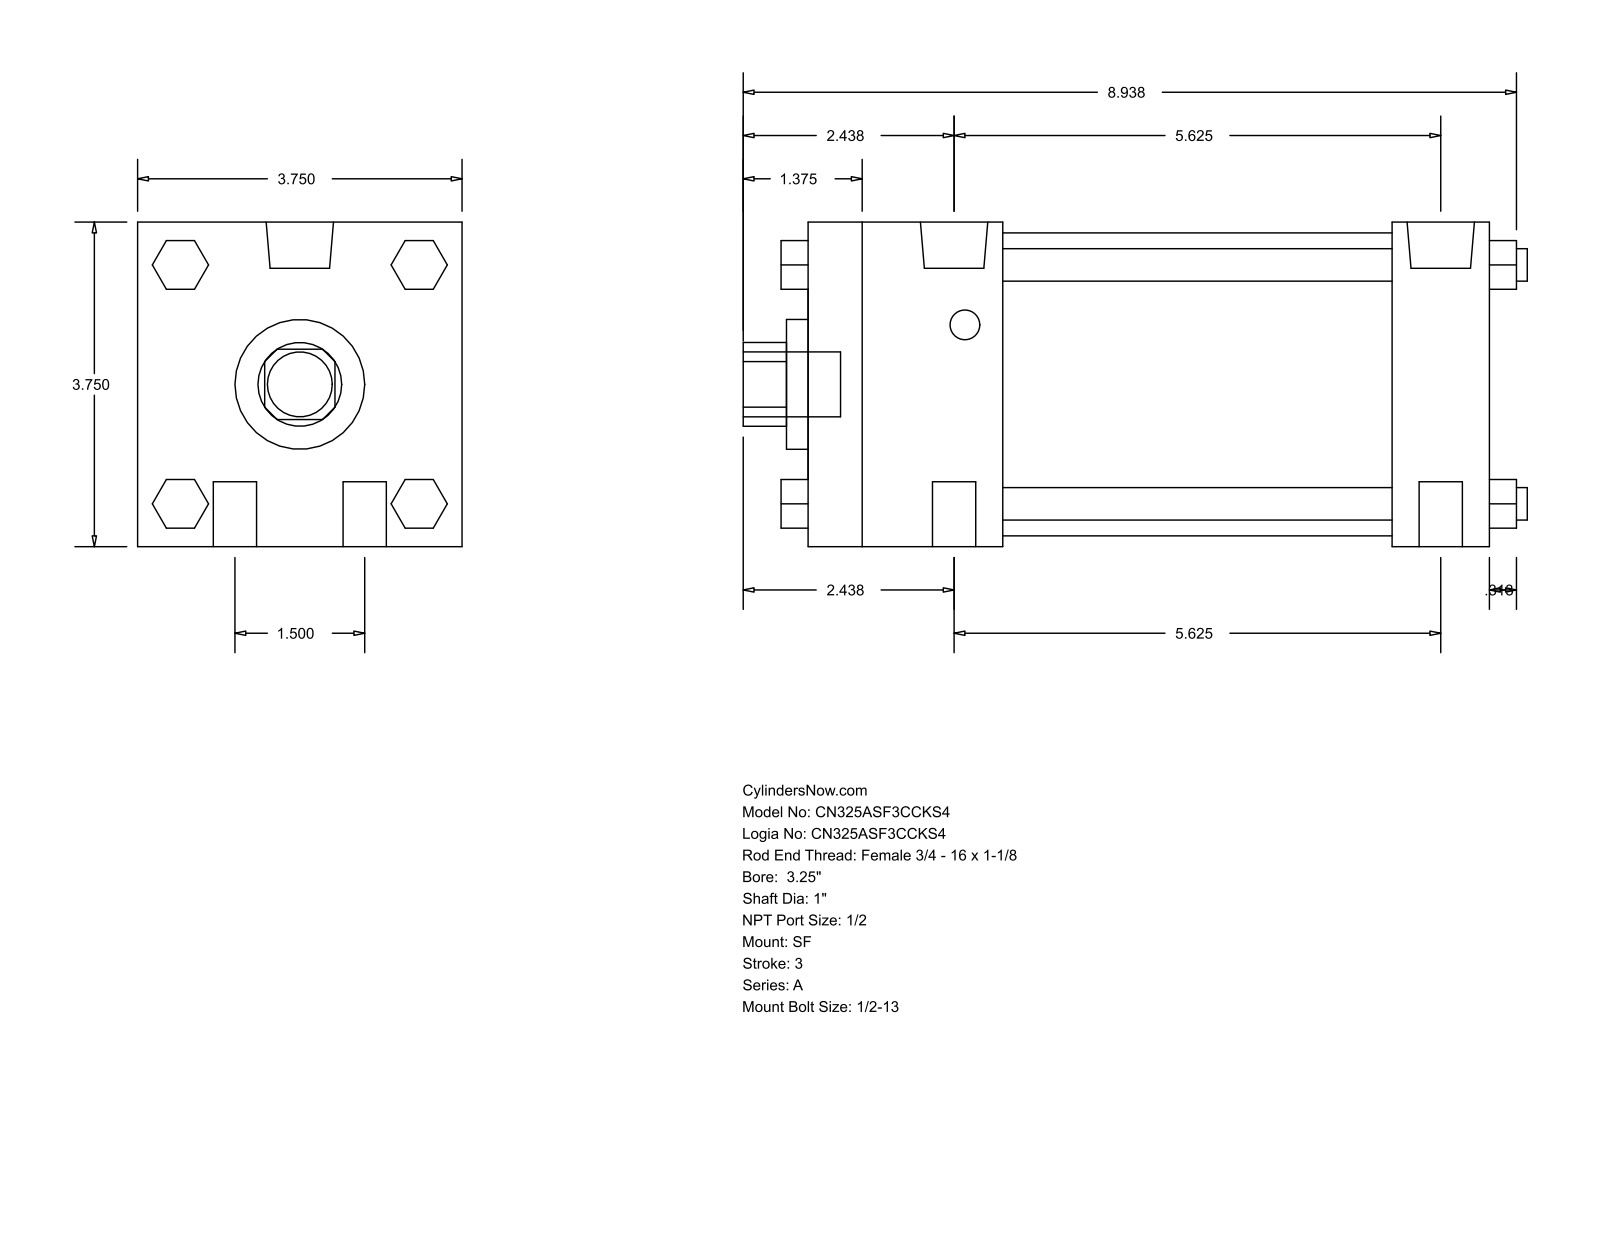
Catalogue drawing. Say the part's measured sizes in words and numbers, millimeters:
The part is named "A_SF__0325_1". Its 3-D file was written by "GSSL Pune (CONFIG_CONTROL_DESIGN)". It is 0 solids with 124 faces: 94 planar, 30 cylindrical and 0 other. Overall it measures 230.19 by 95.25 by 95.25 millimeters. Round holes: 1 of diameter 25.4, 1 of diameter 38.1, 1 of diameter 88.9. Round bosses or shafts: 4 of diameter 12.7, 4 of diameter 9.53, 2 of diameter 19.77, 2 of diameter 8.73, 1 of diameter 19.05. Partial cylindrical surfaces (rounded edges, fillets, slot ends): 1 of radius 12.29. The main face-to-face distances are 95.24, 200.02, 28.57, 171.45, 57.15, 114.3, 142.87, 14.28, 35.05, 60.71.
